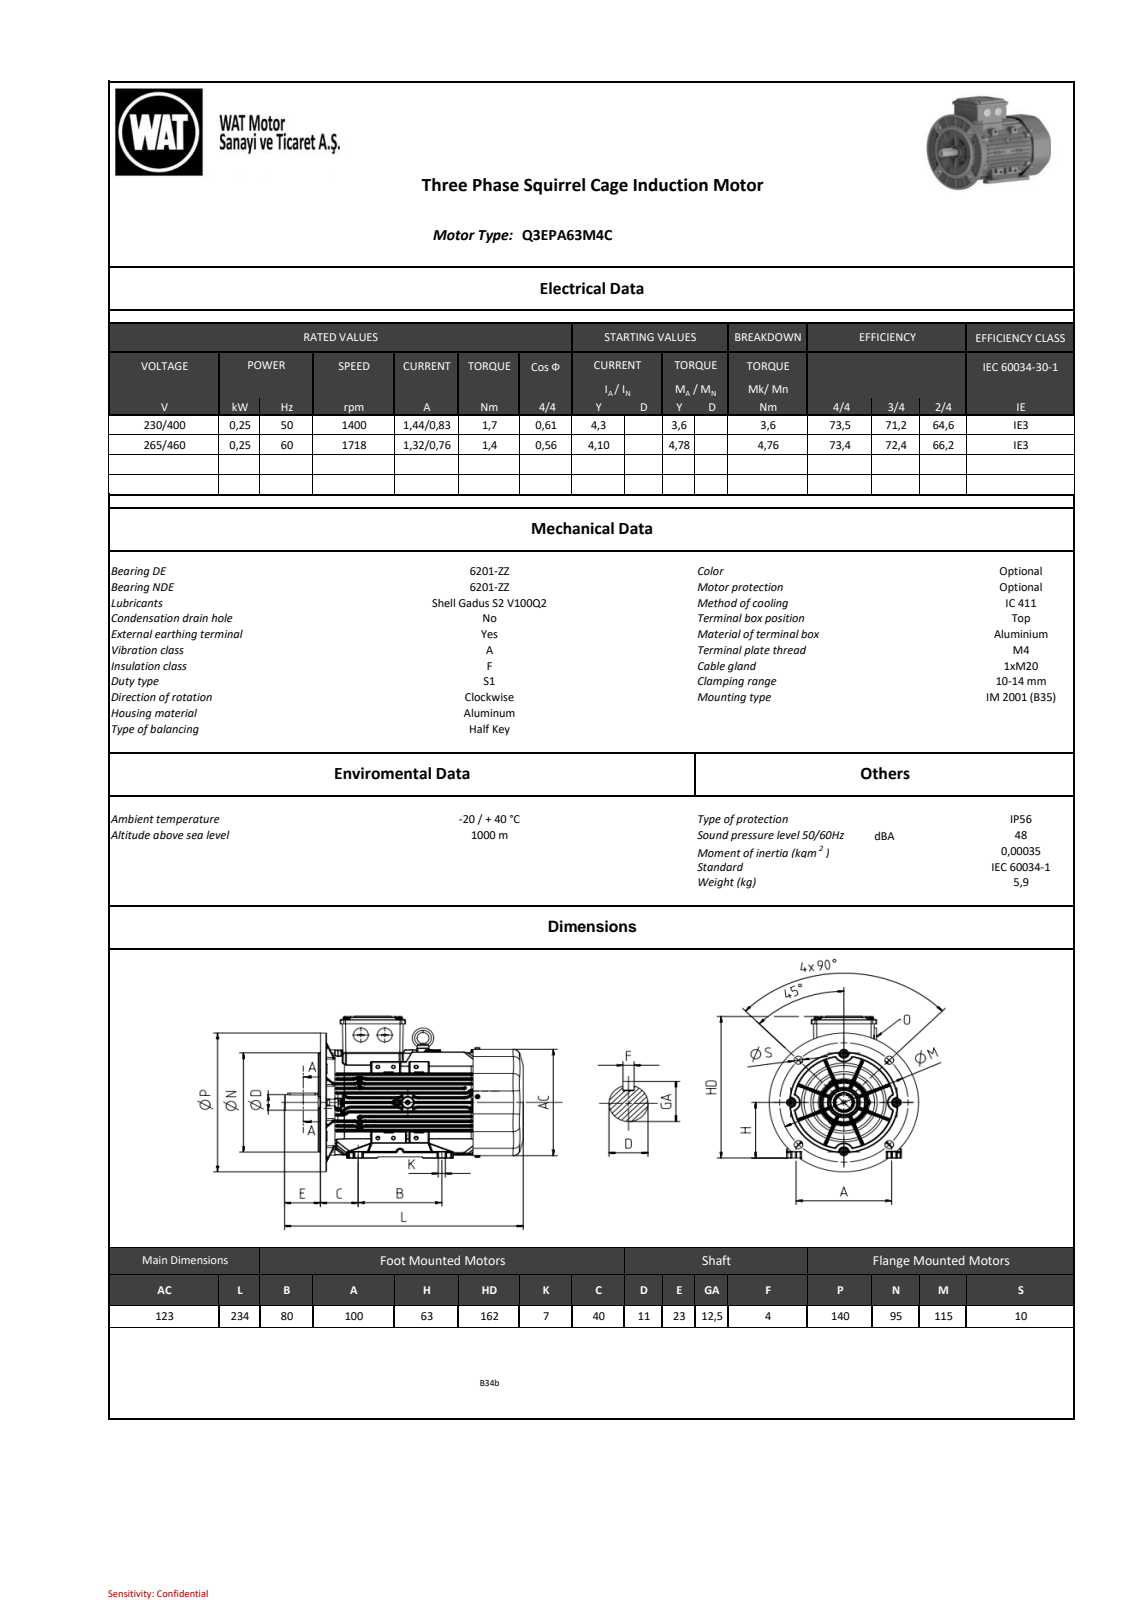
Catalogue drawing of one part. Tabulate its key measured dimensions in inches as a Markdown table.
| quantity | value |
| --- | --- |
| part name | QE Series_ 63_B35_Deep Cover__stp_objects |
| STEP written by | SIEMENS PLM Software NX2206.8101 (AP203_CONFIGURATION_CONTROLLED_3D_DESIGN_OF_MECHANICAL_PARTS_AND_ASSEMBLIES_MIM_LF) |
| units | inches |
| bodies | 0 solids, 1519 faces (851 planar, 467 cylindrical, 201 other) |
| overall size | 9.192 × 6.661 × 5.52 |
| round holes (diameter × count) | 0.394 × 8, 0.098 × 4, 0.144 × 4, 0.165 × 4, 0.118 × 2, 0.276 × 2, 0.197 × 1, 0.315 × 1, 0.589 × 1, 0.748 × 1, 0.781 × 1, 2.244 × 1 |
| round bosses / shafts (diameter × count) | 0.315 × 8, 0.189 × 4, 0.157 × 3, 5.52 × 1, 4.843 × 1, 3.74 × 1, 2.402 × 1, 0.995 × 1 |
| partial cylindrical surfaces (radius × count) | 0.02 × 112, 0.039 × 110, 0.059 × 16, 0.079 × 12, 0.157 × 8, 0.197 × 7, 0.315 × 7, 0.012 × 6 |
| main face-to-face distances | 0.276, 1.101, 0.197, 0.039, 1.104, 0.413, 0.157, 0.273, 0.544, 0.271 |
| hole center spacings | 1.733, 2.264, 3.202, 2.126, 4.183, 4.183, 4.528, 0.394 |
